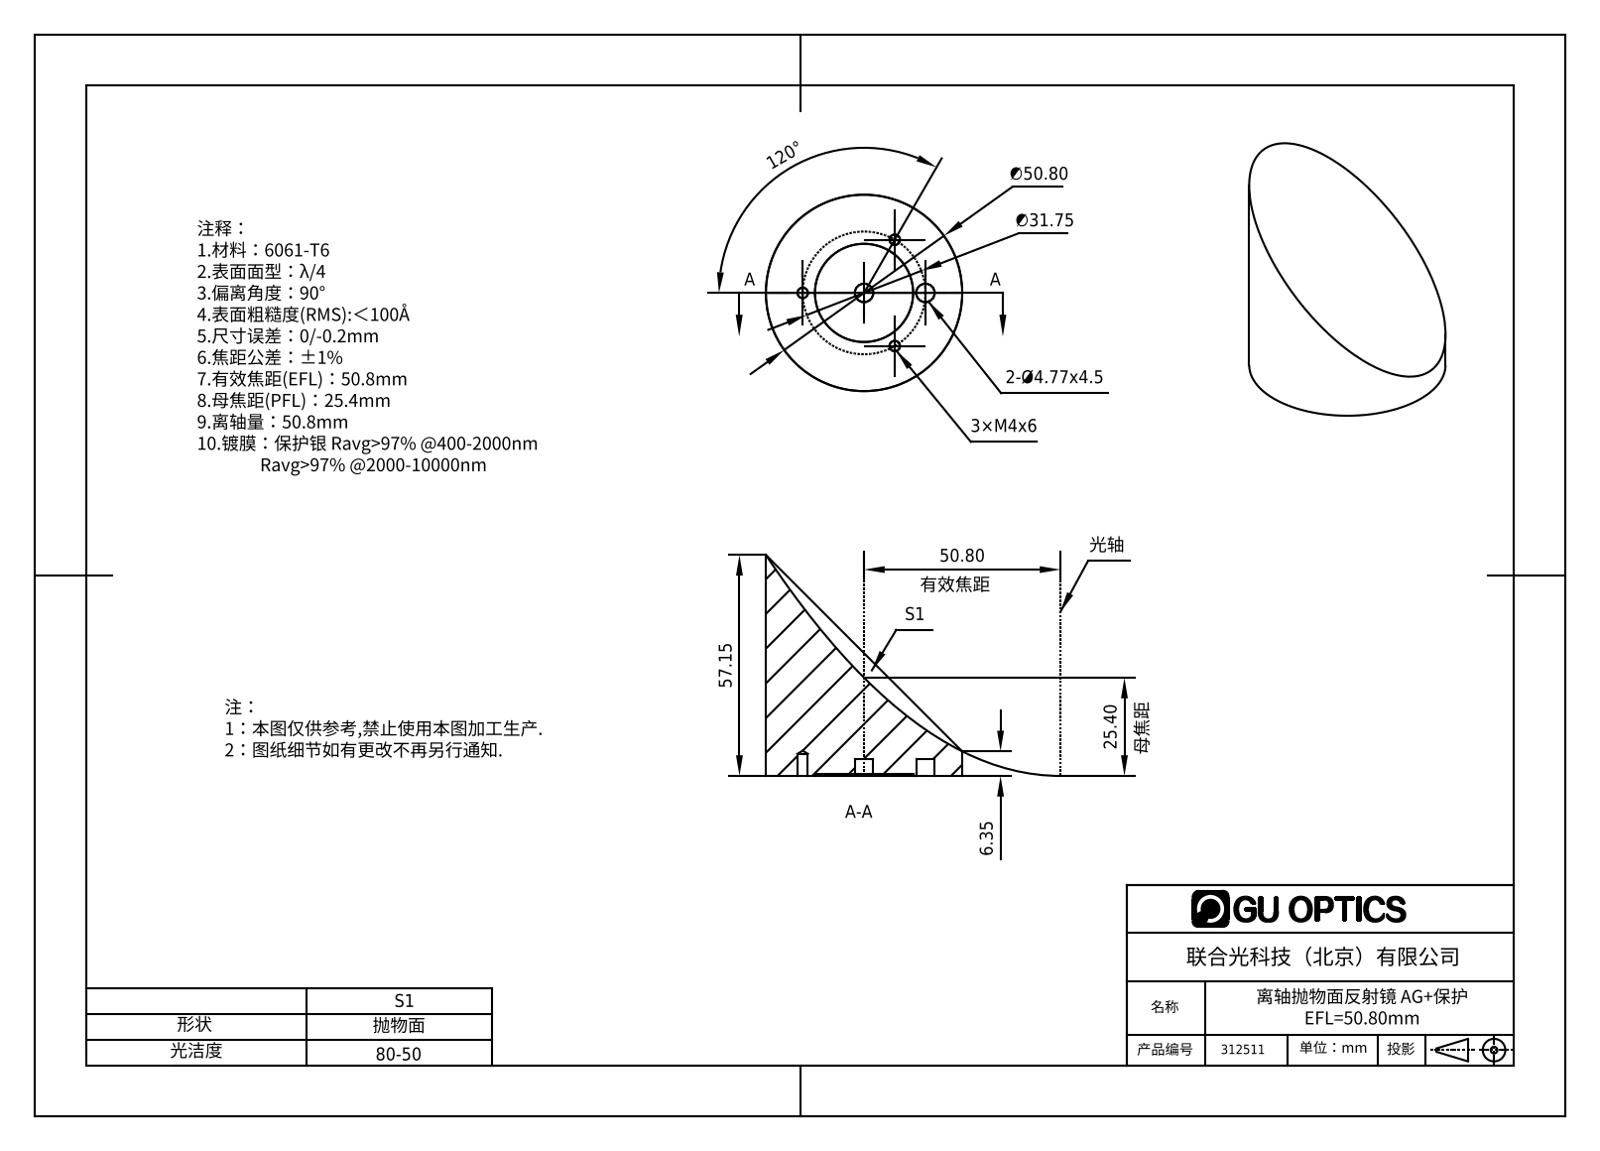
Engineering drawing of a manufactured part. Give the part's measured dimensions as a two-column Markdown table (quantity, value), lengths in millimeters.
| quantity | value |
| --- | --- |
| part name | Ø50_36594 |
| STEP written by | SolidWorks 2018 (CONFIG_CONTROL_DESIGN) |
| units | millimeters |
| bodies | 1 solid, 26 faces (4 planar, 14 cylindrical, 8 other) |
| overall size | 57.15 × 50.8 × 50.8 |
| volume | 57 411 mm³ |
| surface area | 10 338 mm² |
| round holes (diameter × count) | 2.71 × 3, 4.77 × 1, 4.78 × 1, 25.4 × 1 |
| round bosses / shafts (diameter × count) | 50.8 × 1 |
| main face-to-face distances | 0.51, 4.32, 3.81 |
| hole center spacings | 15.88, 27.5, 31.76 |
